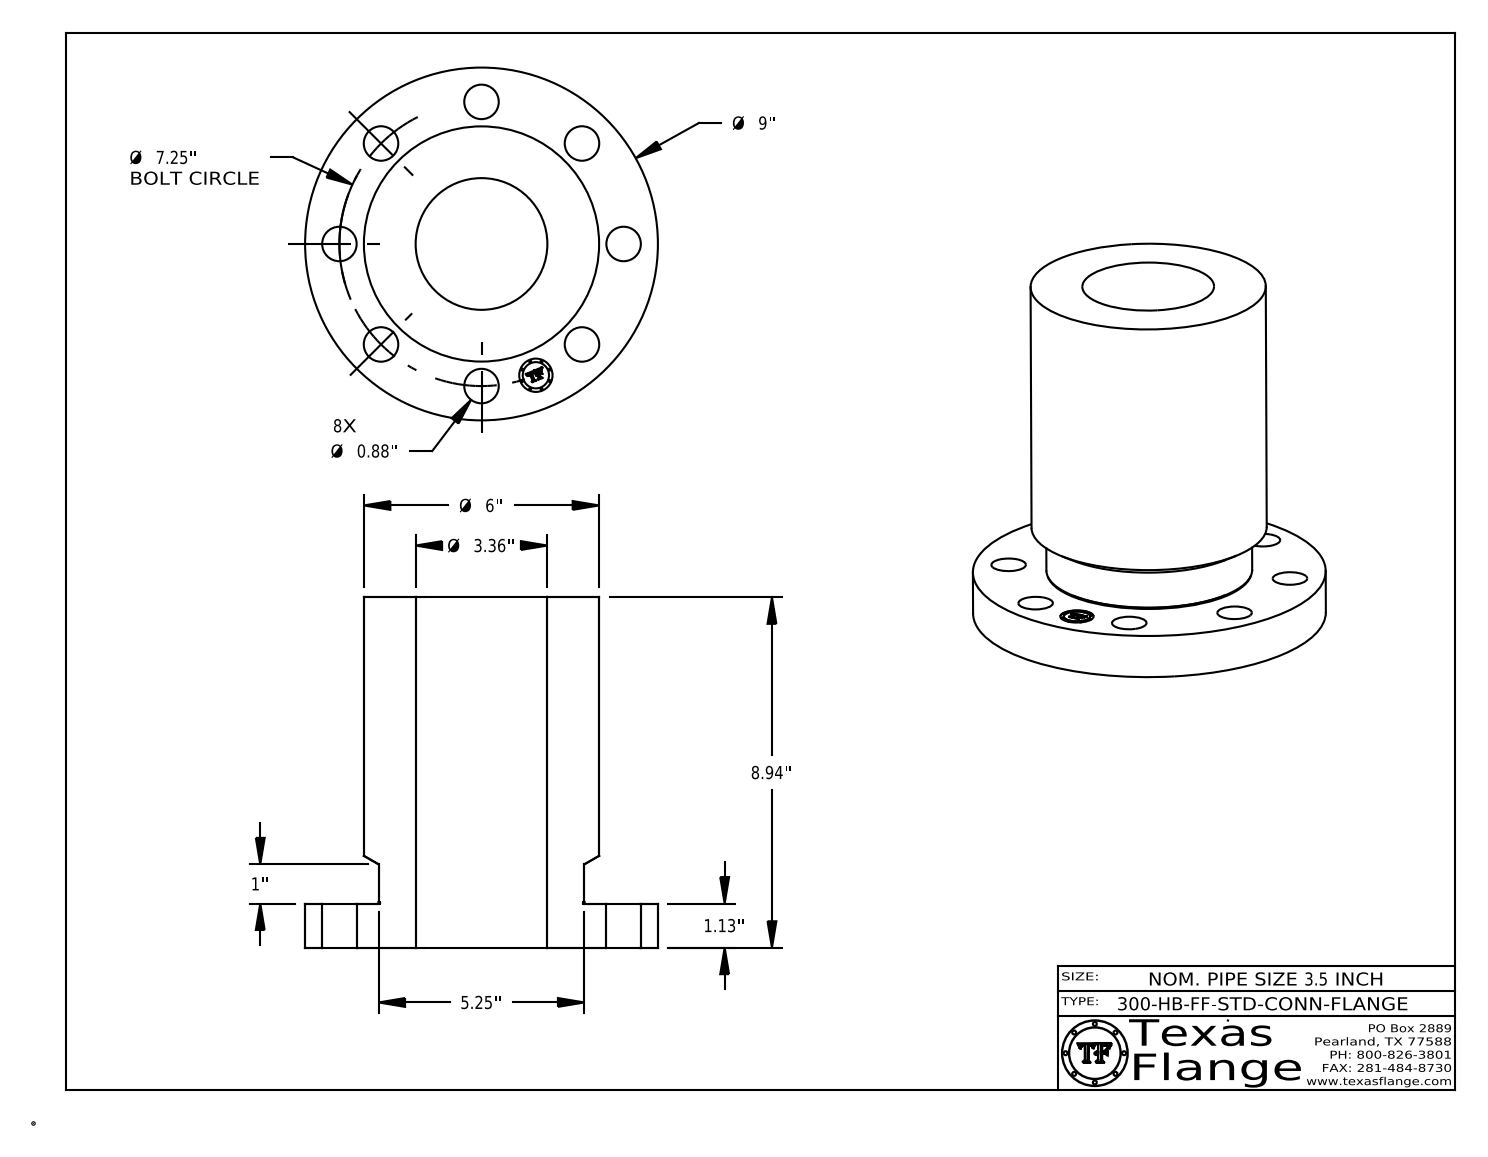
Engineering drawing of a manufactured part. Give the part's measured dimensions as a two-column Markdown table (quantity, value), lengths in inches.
| quantity | value |
| --- | --- |
| part name | 3.5-300-HB-FF-STD-CONN-FLANGE |
| STEP written by | CATIA V5 STEP AP214 (AUTOMOTIVE_DESIGN) |
| units | inches |
| bodies | 1 solid, 418 faces (368 planar, 44 cylindrical, 6 other) |
| overall size | 9 × 9 × 8.938 |
| volume | 200.4 in³ |
| surface area | 406.7 in² |
| round holes (diameter × count) | 0.88 × 8, 0.85 × 1, 3.36 × 1 |
| round bosses / shafts (diameter × count) | 0.051 × 8, 9 × 1, 6 × 1, 5.25 × 1, 0.67 × 1 |
| main face-to-face distances | 1.128, 8.937, 7.81, 1.122, 7.815, 0.254, 0.248, 0.016, 0.046, 0.165 |
| hole center spacings | 3.625, 2.774, 5.127, 6.698, 7.25, 1.415, 7.111, 4.028 |
